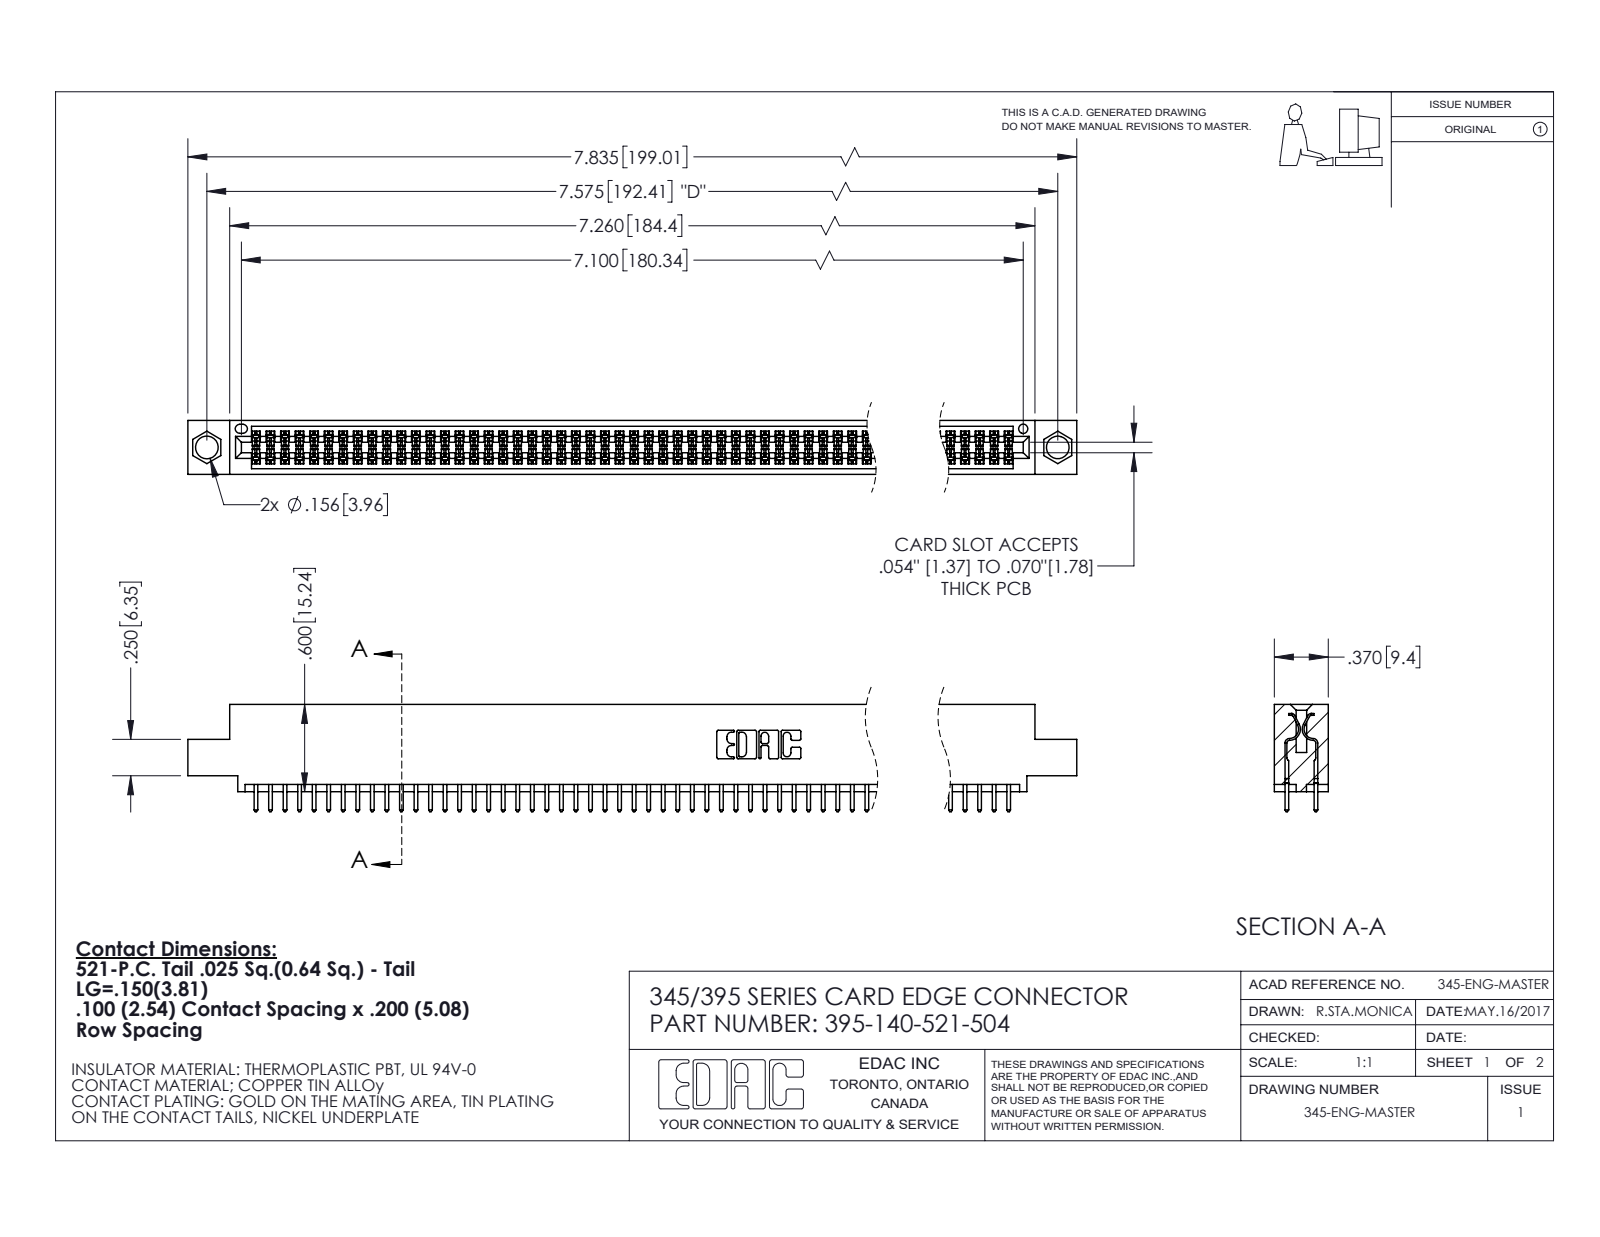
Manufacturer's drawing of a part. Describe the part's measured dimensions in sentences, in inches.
The part is named "345-292-001_345-293-121; 395-140-521-504; 345 Part_0.110 Offset - 0.156 Dia-TI". Its 3-D file was written by "SolidWorks 2020 (CONFIG_CONTROL_DESIGN)". It is 141 solids with 7144 faces: 4718 planar, 2426 cylindrical and 0 other. Overall it measures 7.835 by 0.737 by 0.37 inches. Its volume is 1.181 cubic inches and its surface area 44.52 square inches. Round holes: 2 of diameter 0.156, 1 of diameter 0.064. Partial cylindrical surfaces (rounded edges, fillets, slot ends): 210 of radius 0.006, 140 of radius 0.01, 22 of radius 0.01, 6 of radius 0.007, 6 of radius 0.031, 3 of radius 0.026, 2 of radius 0.014, 2 of radius 0.019. The main face-to-face distances are 0.072, 0.298, 0.2, 0.098, 0.272, 0.025, 0.37, 0.225, 0.175, 0.149. The hole center spacings are 0.27, 7.339, 7.575.
